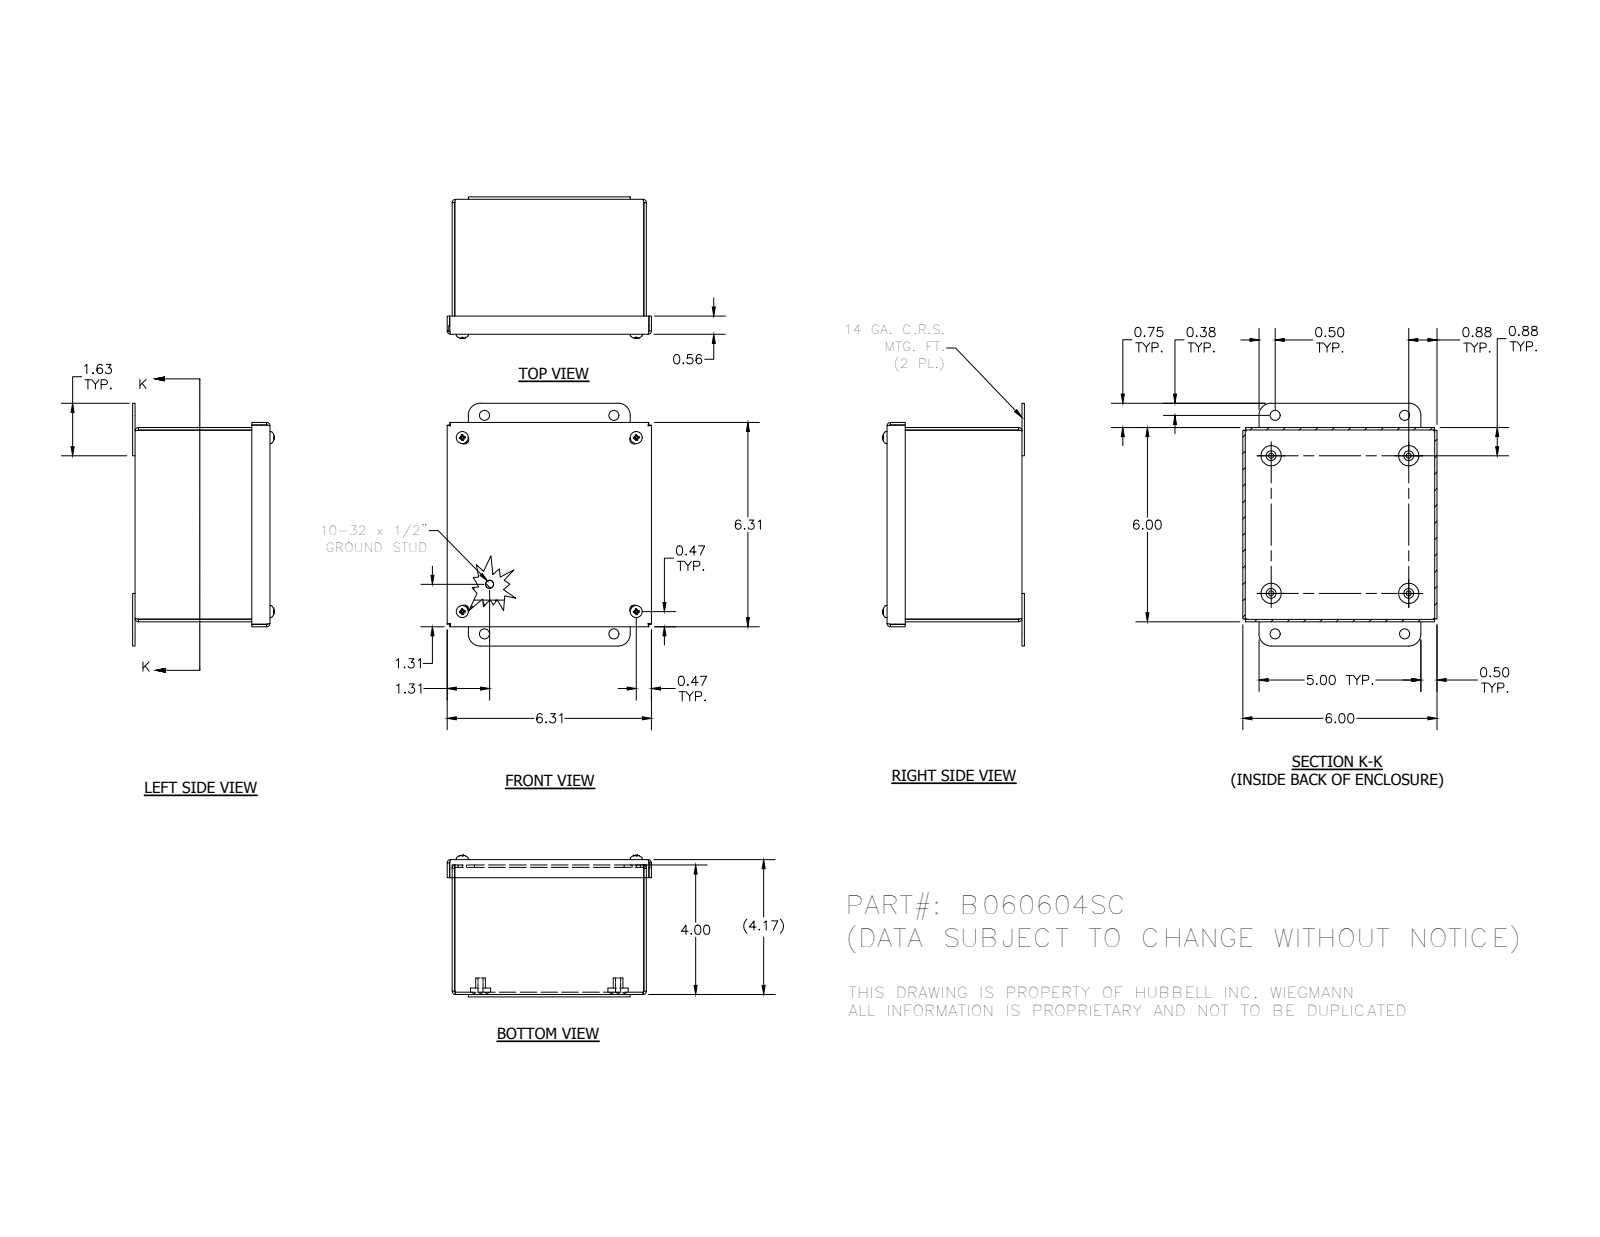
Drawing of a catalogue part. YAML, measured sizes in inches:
part_name: "B060604SC; 3482; 34984; B060604SCBKP (+6 more)"
step_written_by: "Autodesk Inventor 2012 (AUTOMOTIVE_DESIGN)"
units: inches
bodies: {solids: 23, faces: 532, planar: 311, cylindrical: 102, other: 119}
overall_size: [7.5, 6.313, 4.346]
volume: 18.15
surface_area: 462.3
round_holes:
  - {diameter: 0.145, count: 4}
  - {diameter: 0.156, count: 4}
  - {diameter: 0.196, count: 4}
  - {diameter: 0.278, count: 4}
  - {diameter: 0.281, count: 4}
  - {diameter: 0.31, count: 4}
  - {diameter: 0.313, count: 4}
round_bosses_or_shafts:
  - {diameter: 0.19, count: 5}
  - {diameter: 0.625, count: 4}
  - {diameter: 0.453, count: 4}
  - {diameter: 0.406, count: 4}
  - {diameter: 0.373, count: 4}
  - {diameter: 0.3, count: 4}
  - {diameter: 0.248, count: 4}
  - {diameter: 0.25, count: 1}
partial_cylinders:
  - {radius: 0.031, count: 12}
  - {radius: 0.105, count: 12}
  - {radius: 0.089, count: 4}
  - {radius: 0.375, count: 4}
face_to_face_distances: [0.074, 5.926, 4.094, 6, 5.852, 4.168, 4.02, 0.187, 3.906, 3.832]
hole_center_spacings: [5.314, 4.845, 5.374, 5.375, 0.972, 5.395, 6.101, 7.515]
